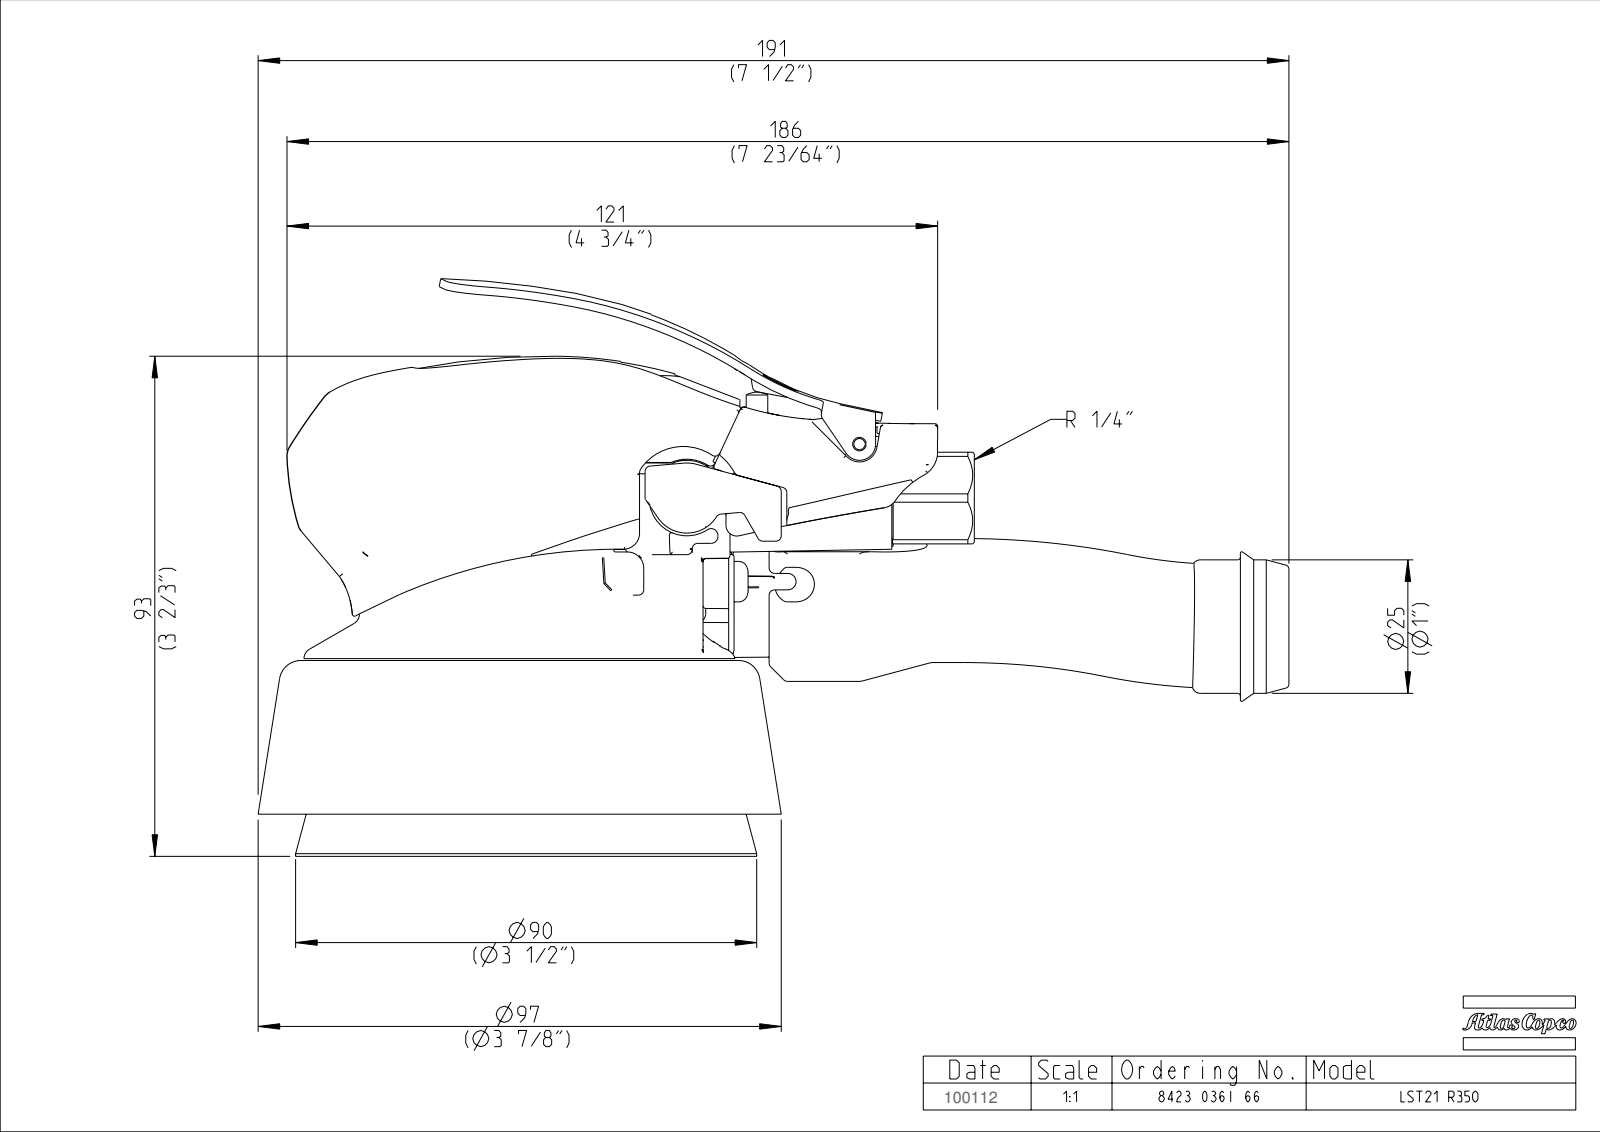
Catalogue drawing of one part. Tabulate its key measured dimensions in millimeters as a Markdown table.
| quantity | value |
| --- | --- |
| part name | TMP10434_SW |
| STEP written by | PRO/ENGINEER BY PARAMETRIC TECHNOLOGY CORPORATION, 2008310 (CONFIG_CONTROL_DESIGN) |
| units | millimeters |
| bodies | 0 solids, 731 faces (123 planar, 179 cylindrical, 429 other) |
| overall size | 191.14 × 107.13 × 97 |
| round bosses / shafts (diameter × count) | 7.5 × 2, 85.5 × 1, 24.75 × 1, 23 × 1, 4 × 1, 2.5 × 1 |
| partial cylindrical surfaces (radius × count) | 1 × 36, 0.5 × 34, 0.3 × 7, 0.6 × 6, 1.5 × 6, 3 × 6, 0.25 × 5, 5 × 4 |
| main face-to-face distances | 7.82, 28.5, 36.32, 64.64, 9, 29.25, 93.89, 17, 102.89, 73.64 |
